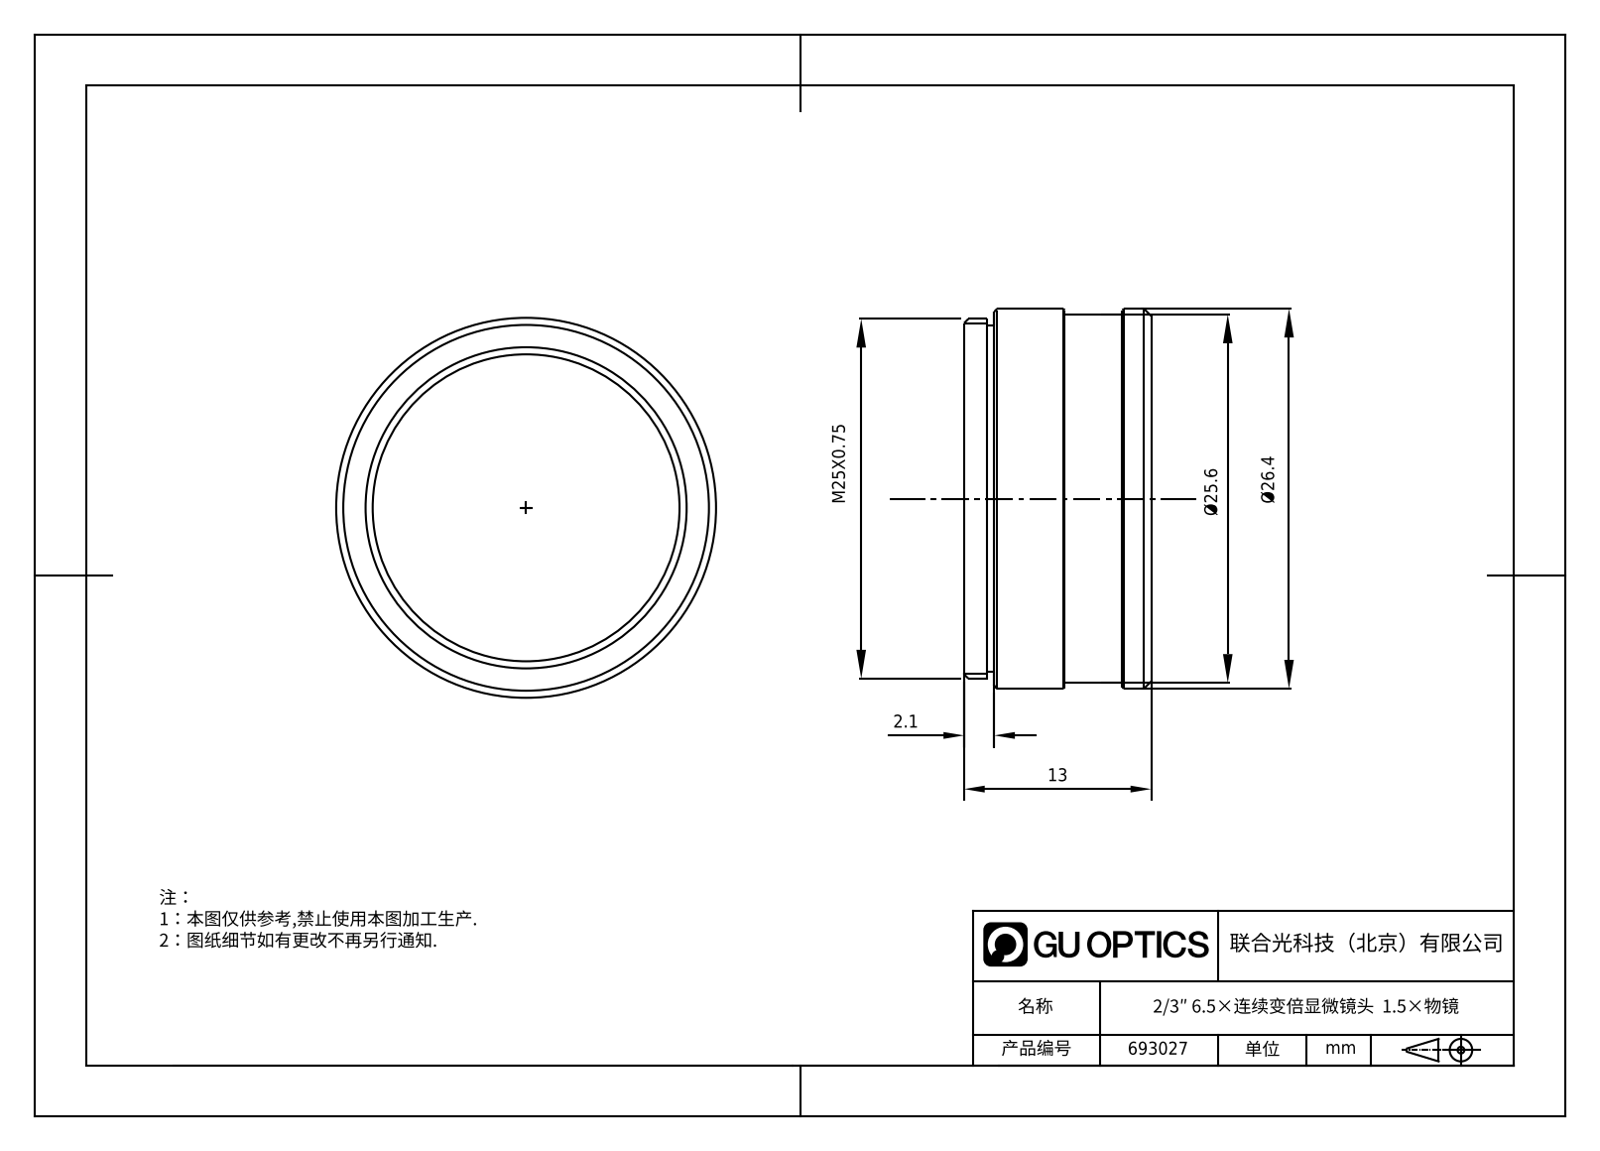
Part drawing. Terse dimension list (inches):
name: 66115
written by: SolidWorks 2017 (CONFIG_CONTROL_DESIGN)
unit: in
bodies: 1 solid, 43 faces (9 planar, 18 cylindrical, 16 other)
size: 1.039 × 1.039 × 0.512
volume: 0.256 in³; area: 4.201 in²
holes: 1× ⌀0.74, 1× ⌀0.78, 1× ⌀0.846, 1× ⌀0.89
bosses: 1× ⌀1.039, 1× ⌀1.008, 1× ⌀0.984, 1× ⌀0.949
face distances: 0.429, 0.512, 0.083, 0.331, 0.098, 0.181, 0.335, 0.094, 0.177, 0.449
